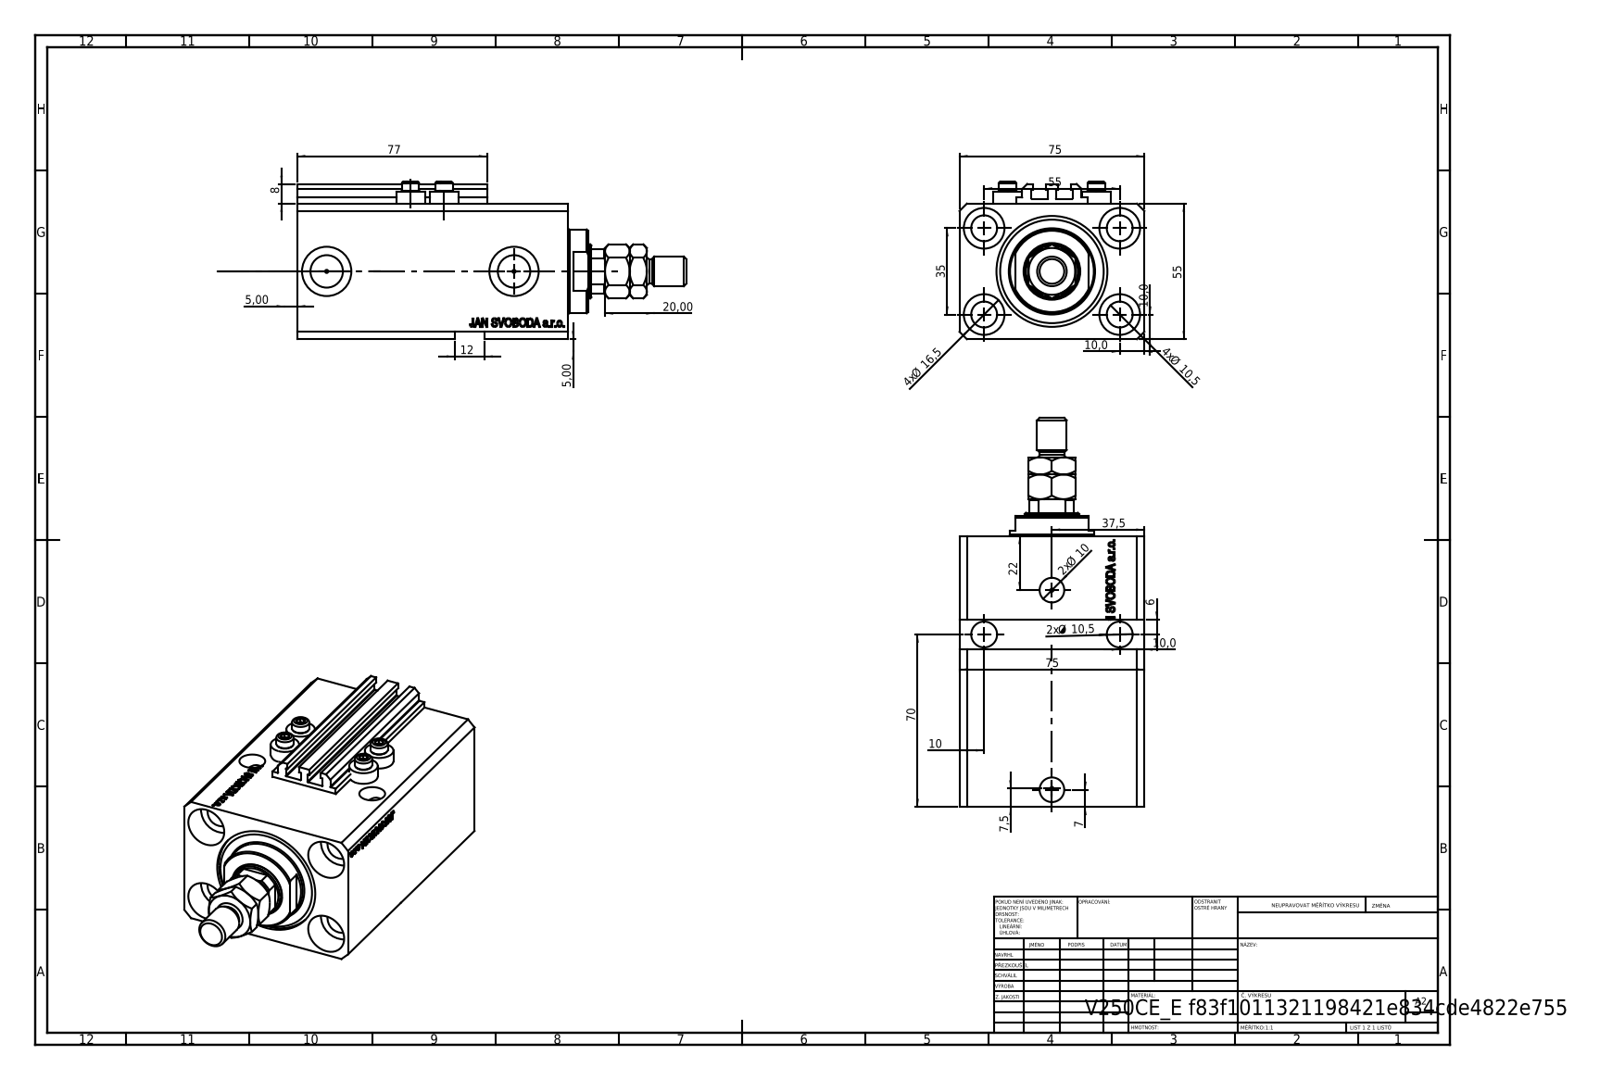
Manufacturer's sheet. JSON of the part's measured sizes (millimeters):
{"part_name": "V250CE_VC_E; ALLEN BOLT V250CE; MTA; V250CE_C_VCP (+1 more)", "step_written_by": "SolidWorks 2019 (CONFIG_CONTROL_DESIGN)", "units": "millimeters", "bodies": {"solids": 9, "faces": 1113, "planar": 529, "cylindrical": 130, "other": 454}, "overall_size": [157.9, 75, 64], "volume_mm3": 394729, "surface_area_mm2": 99045, "round_holes": [[10.5, 7], [1.25, 4], [4, 4], [16.5, 4], [10, 2], [13.16, 2], [20, 2], [22, 1], [32, 1], [45, 1]], "round_bosses_or_shafts": [[11.6, 4], [7, 4], [34, 1], [12, 1], [10, 1]], "partial_cylinders_radius": [[0.2, 10], [10.5, 1]], "face_to_face_distances": [55, 75, 110, 82.9, 27.1, 3, 9.9, 73, 100.1, 2.5], "hole_center_spacings": [32.6, 55, 13.6, 14.09, 25.81, 32.87, 33.62, 35]}
